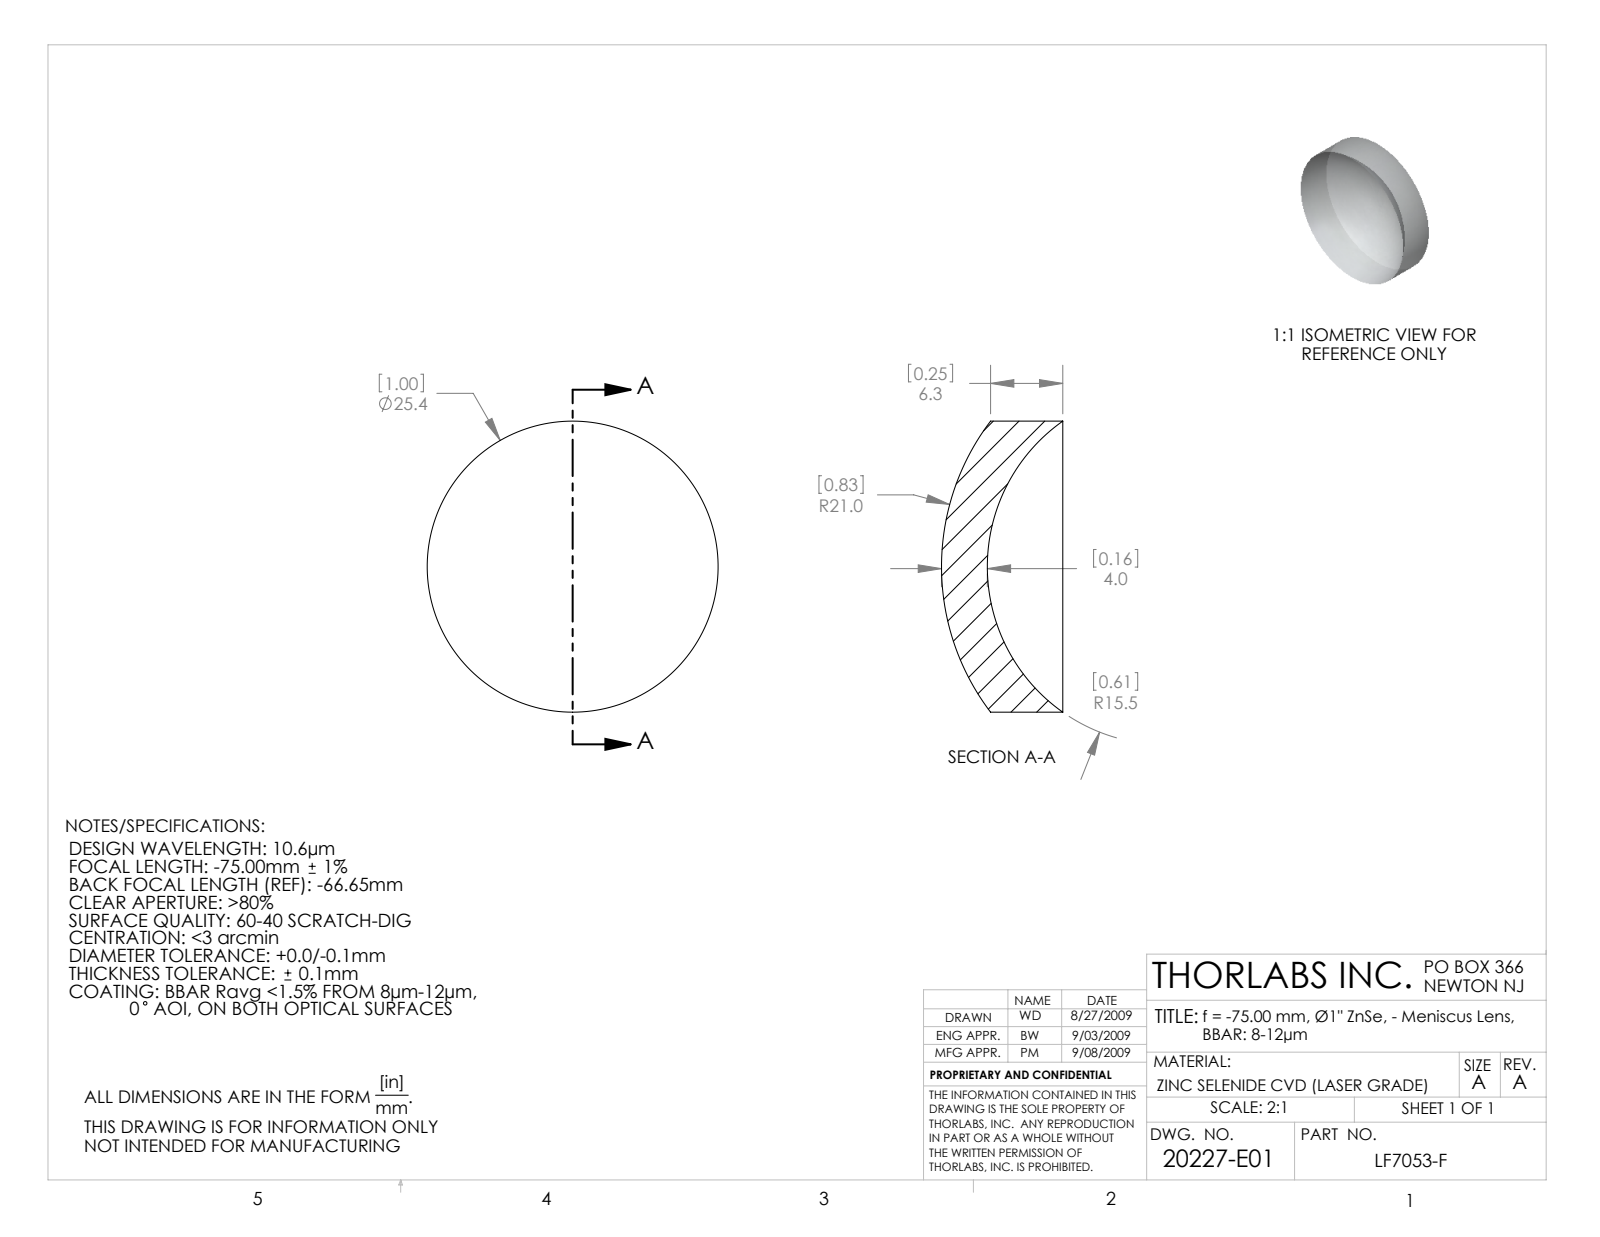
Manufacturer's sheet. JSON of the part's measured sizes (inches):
{"part_name": "20227-E0W", "step_written_by": "SolidWorks 2007 (CONFIG_CONTROL_DESIGN)", "units": "inches", "bodies": {"solids": 1, "faces": 6, "planar": 0, "cylindrical": 2, "other": 4}, "overall_size": [1, 1, 0.417], "volume_in3": 0.153, "surface_area_in2": 2.652, "round_bosses_or_shafts": [[1, 1]]}
